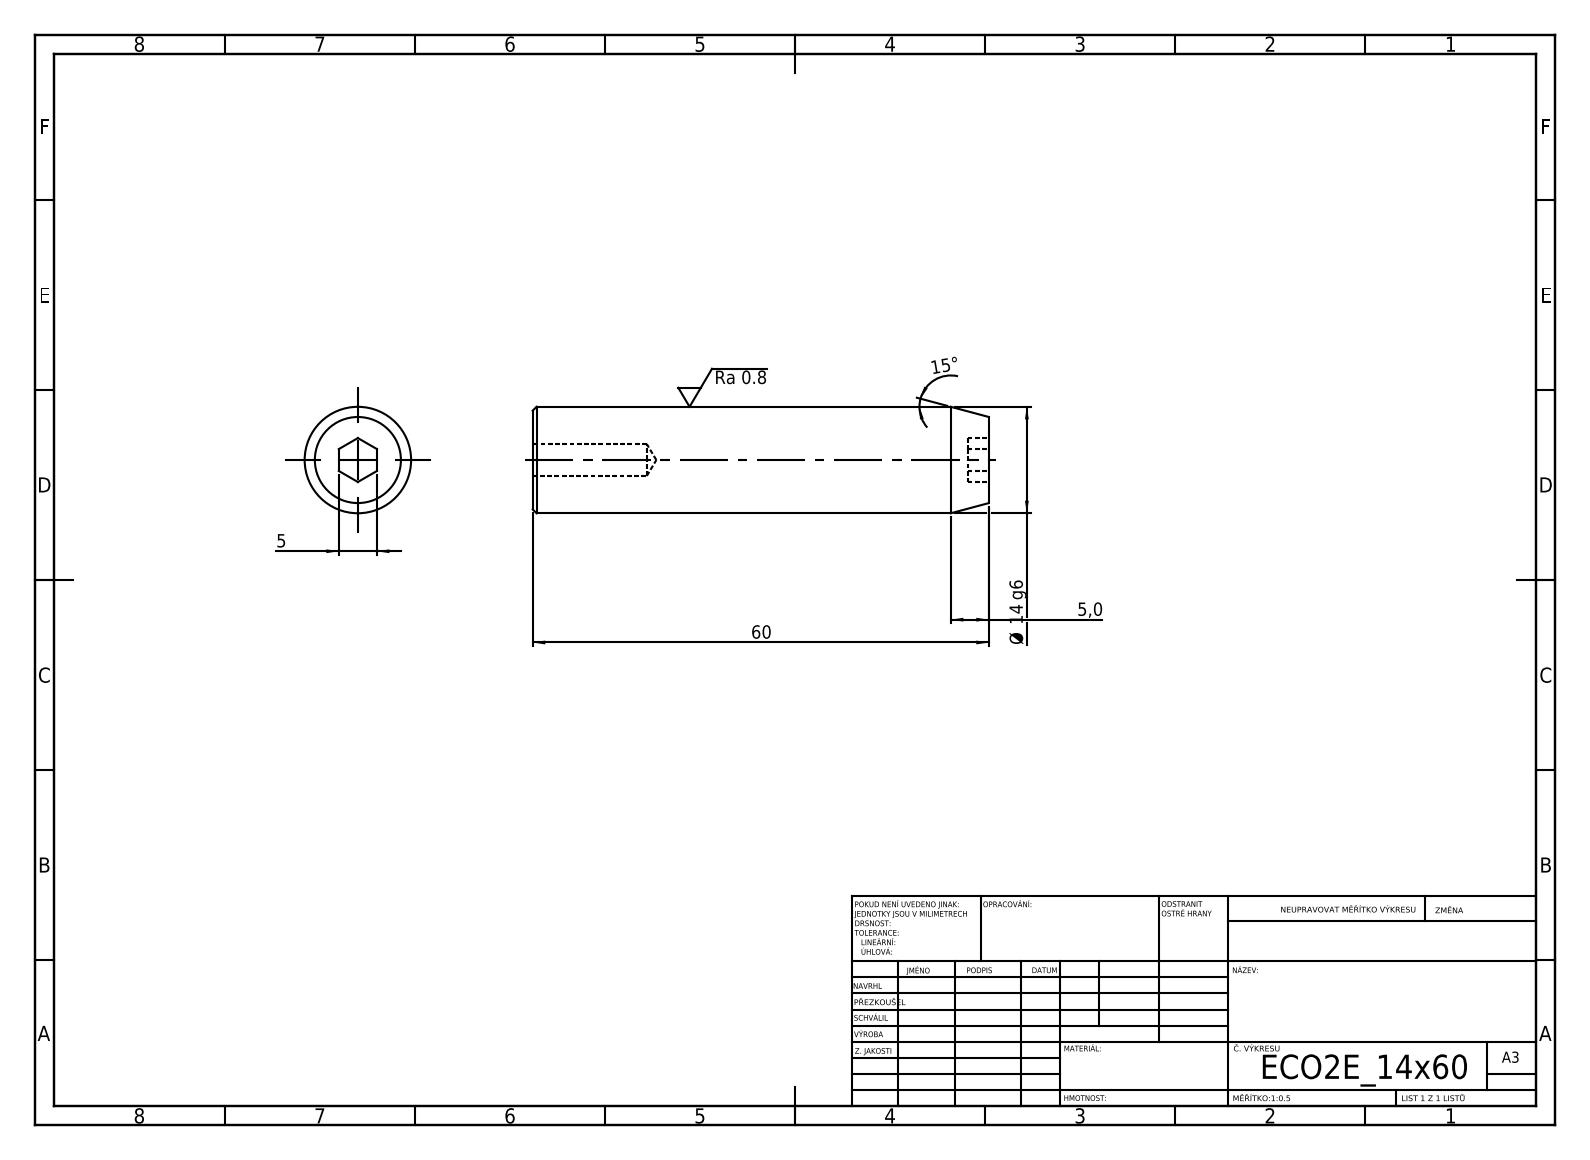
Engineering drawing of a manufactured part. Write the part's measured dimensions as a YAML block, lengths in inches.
step_written_by: "SolidWorks 2019 (CONFIG_CONTROL_DESIGN)"
units: inches
bodies: {solids: 1, faces: 19, planar: 9, cylindrical: 4, other: 6}
overall_size: [2.362, 0.551, 0.551]
volume: 0.538
surface_area: 4.828
round_holes:
  - {diameter: 0.165, count: 1}
round_bosses_or_shafts:
  - {diameter: 0.551, count: 1}
face_to_face_distances: [2.362, 0.197, 0.11, 2.252]
